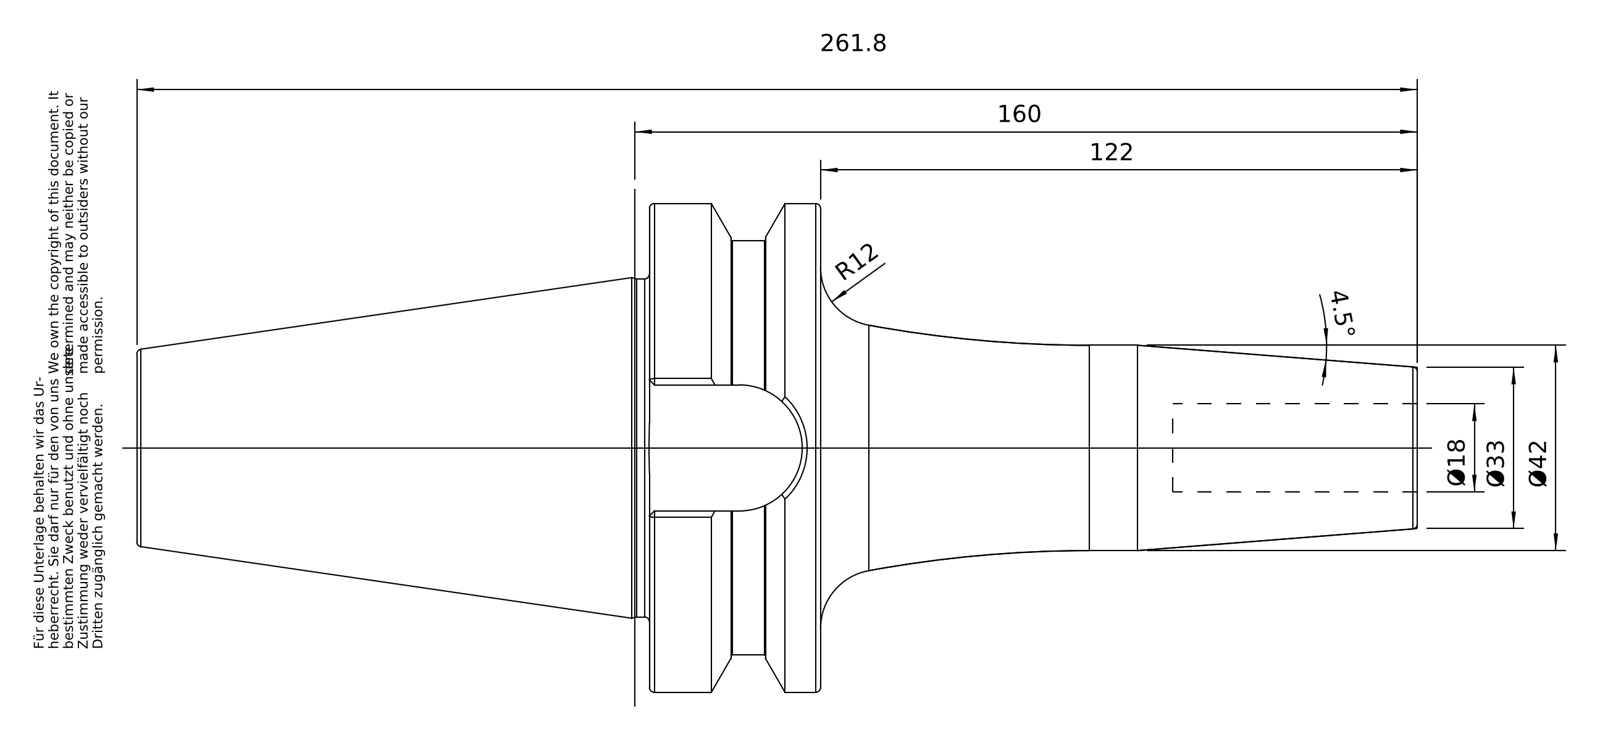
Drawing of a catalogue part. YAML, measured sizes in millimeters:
part_name: "50-642-18"
step_written_by: "PRO/ENGINEER BY PARAMETRIC TECHNOLOGY CORPORATION, 2010430 (CONFIG_CONTROL_DESIGN)"
units: millimeters
bodies: {solids: 1, faces: 98, planar: 26, cylindrical: 22, other: 50}
overall_size: [261.8, 99.97, 99.97]
volume: 628082
surface_area: 68774
round_holes:
  - {diameter: 18, count: 1}
  - {diameter: 20.75, count: 1}
  - {diameter: 25.02, count: 1}
  - {diameter: 25.7, count: 1}
round_bosses_or_shafts:
  - {diameter: 99.97, count: 1}
  - {diameter: 84.75, count: 1}
  - {diameter: 69.15, count: 1}
  - {diameter: 42, count: 1}
  - {diameter: 24.01, count: 1}
partial_cylinders:
  - {radius: 12.9, count: 1}
face_to_face_distances: [35, 70.4, 157, 122, 104.8, 139.8, 261.8, 25.8, 211.8, 107]
